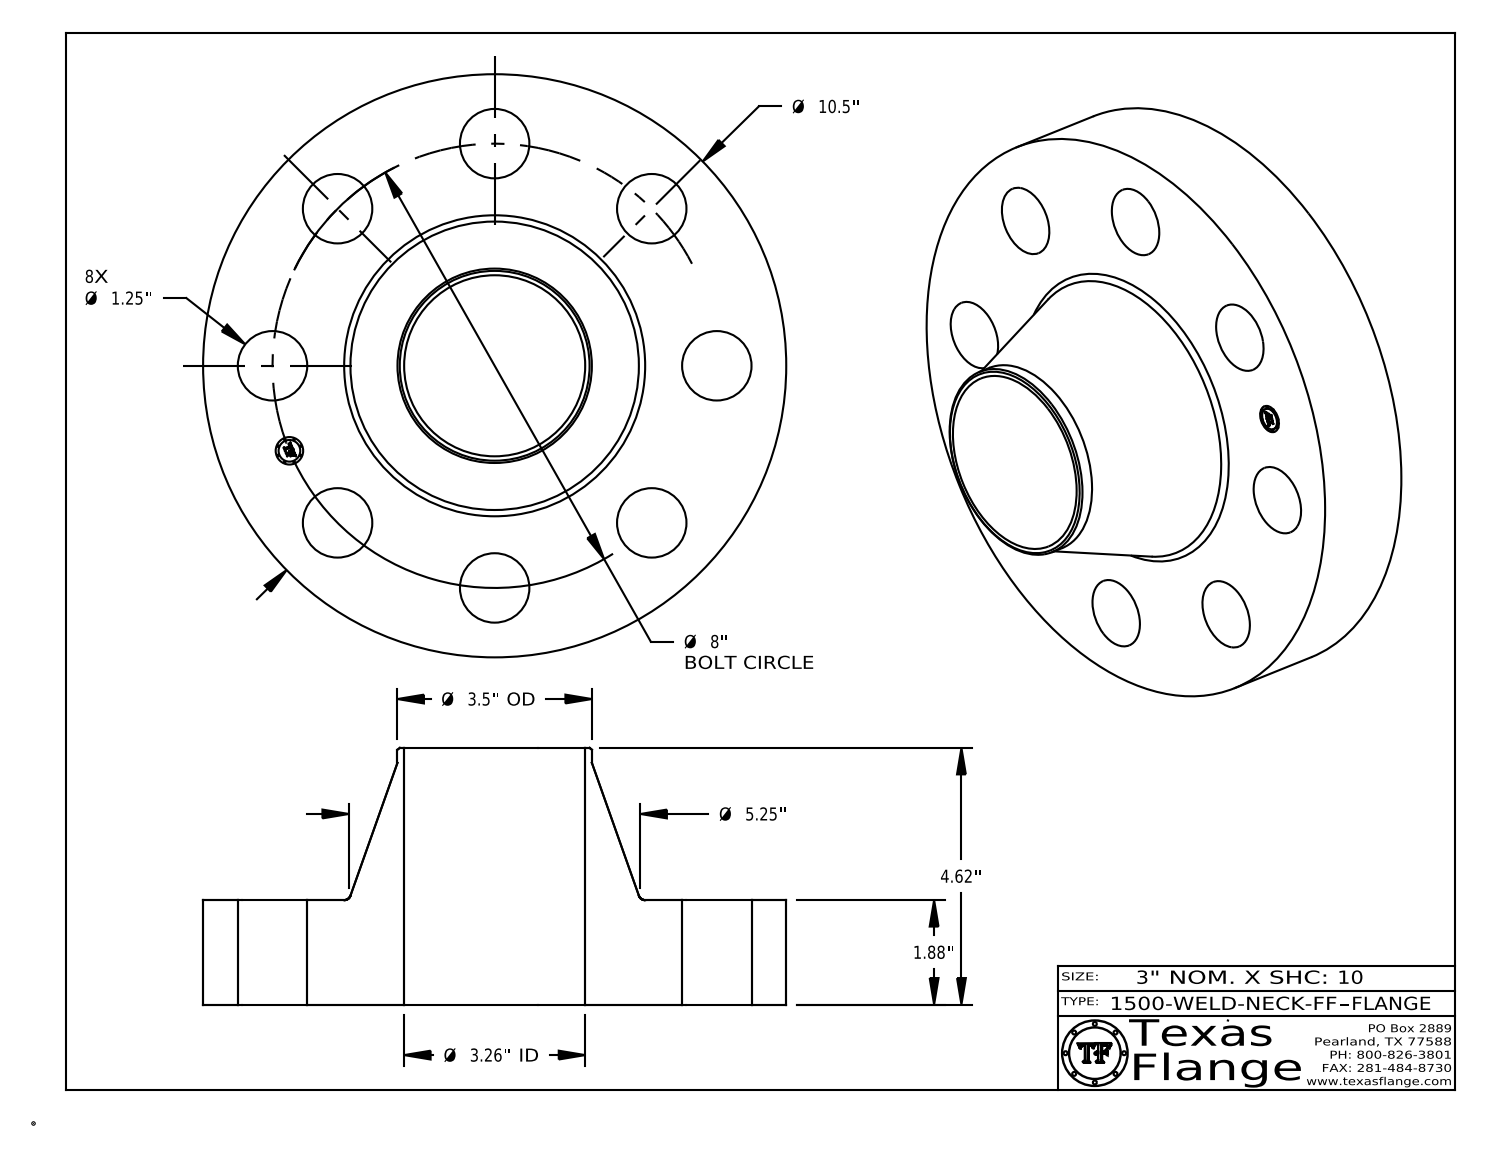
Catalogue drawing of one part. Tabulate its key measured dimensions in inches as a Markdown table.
| quantity | value |
| --- | --- |
| part name | 1500-WELD-NECK-FF |
| STEP written by | CATIA V5 STEP AP214 (AUTOMOTIVE_DESIGN) |
| units | inches |
| bodies | 1 solid, 416 faces (368 planar, 42 cylindrical, 6 other) |
| overall size | 10.5 × 10.5 × 4.62 |
| volume | 146 in³ |
| surface area | 331.7 in² |
| round holes (diameter × count) | 1.25 × 8, 0.495 × 1, 3.26 × 1 |
| round bosses / shafts (diameter × count) | 0.03 × 8, 10.5 × 1, 3.5 × 1, 0.39 × 1 |
| main face-to-face distances | 1.88, 4.62, 2.74, 0.015, 1.865, 2.755, 0.148, 0.145, 0.027, 0.096 |
| hole center spacings | 4, 3.061, 5.657, 7.391, 1.561, 6.652, 7.846, 8 |
